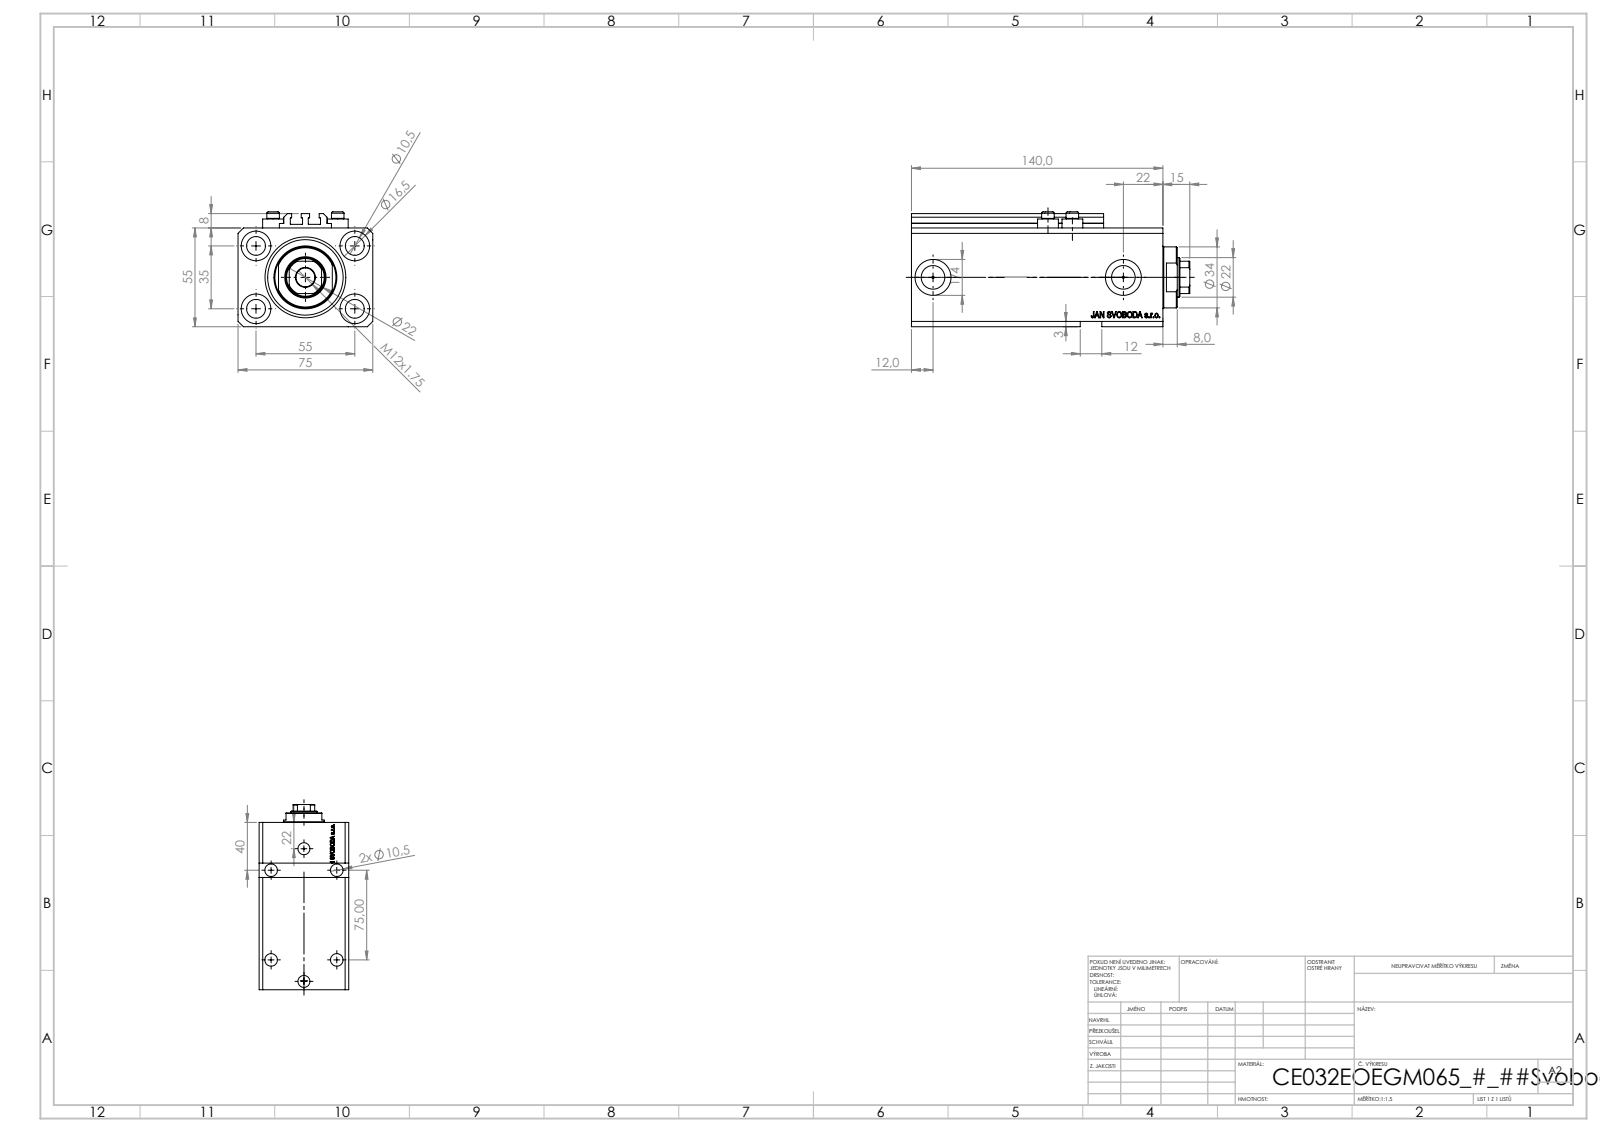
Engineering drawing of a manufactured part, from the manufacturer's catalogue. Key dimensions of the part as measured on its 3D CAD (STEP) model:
Part name (STEP PRODUCT): ALLEN BOLT V250CE; V250CE_E_Body; V250CE_VC_E; V250CE_C_VCP
STEP written by: SolidWorks 2019 (CONFIG_CONTROL_DESIGN)
Units: millimetres
Bodies: 8 solids, 1084 faces (514 planar, 146 cylindrical, 424 other)
Overall size (bounding box): 155 × 75 × 64
Volume: 485 219 mm³ · Surface area: 115 303 mm²
Round holes (diameter × count): ⌀10.5 ×9, ⌀1.25 ×4, ⌀4 ×4, ⌀16.5 ×4, ⌀10 ×2, ⌀13.16 ×2, ⌀20 ×2, ⌀22 ×1, ⌀32 ×1, ⌀45 ×1
Round bosses / shafts (diameter × count): ⌀11.6 ×4, ⌀7 ×4, ⌀34 ×1
Partial cylindrical surfaces — rounded edges, fillets, slot ends (radius × count): R0.2 ×10, R10.5 ×1
Main face-to-face distances: 55, 75, 15, 140, 125, 3, 9.9, 57, 115.1, 130.1
Hole centre spacings: 32.6, 32.87, 55, 96.98, 13.6, 14.09, 25.81, 32.58
